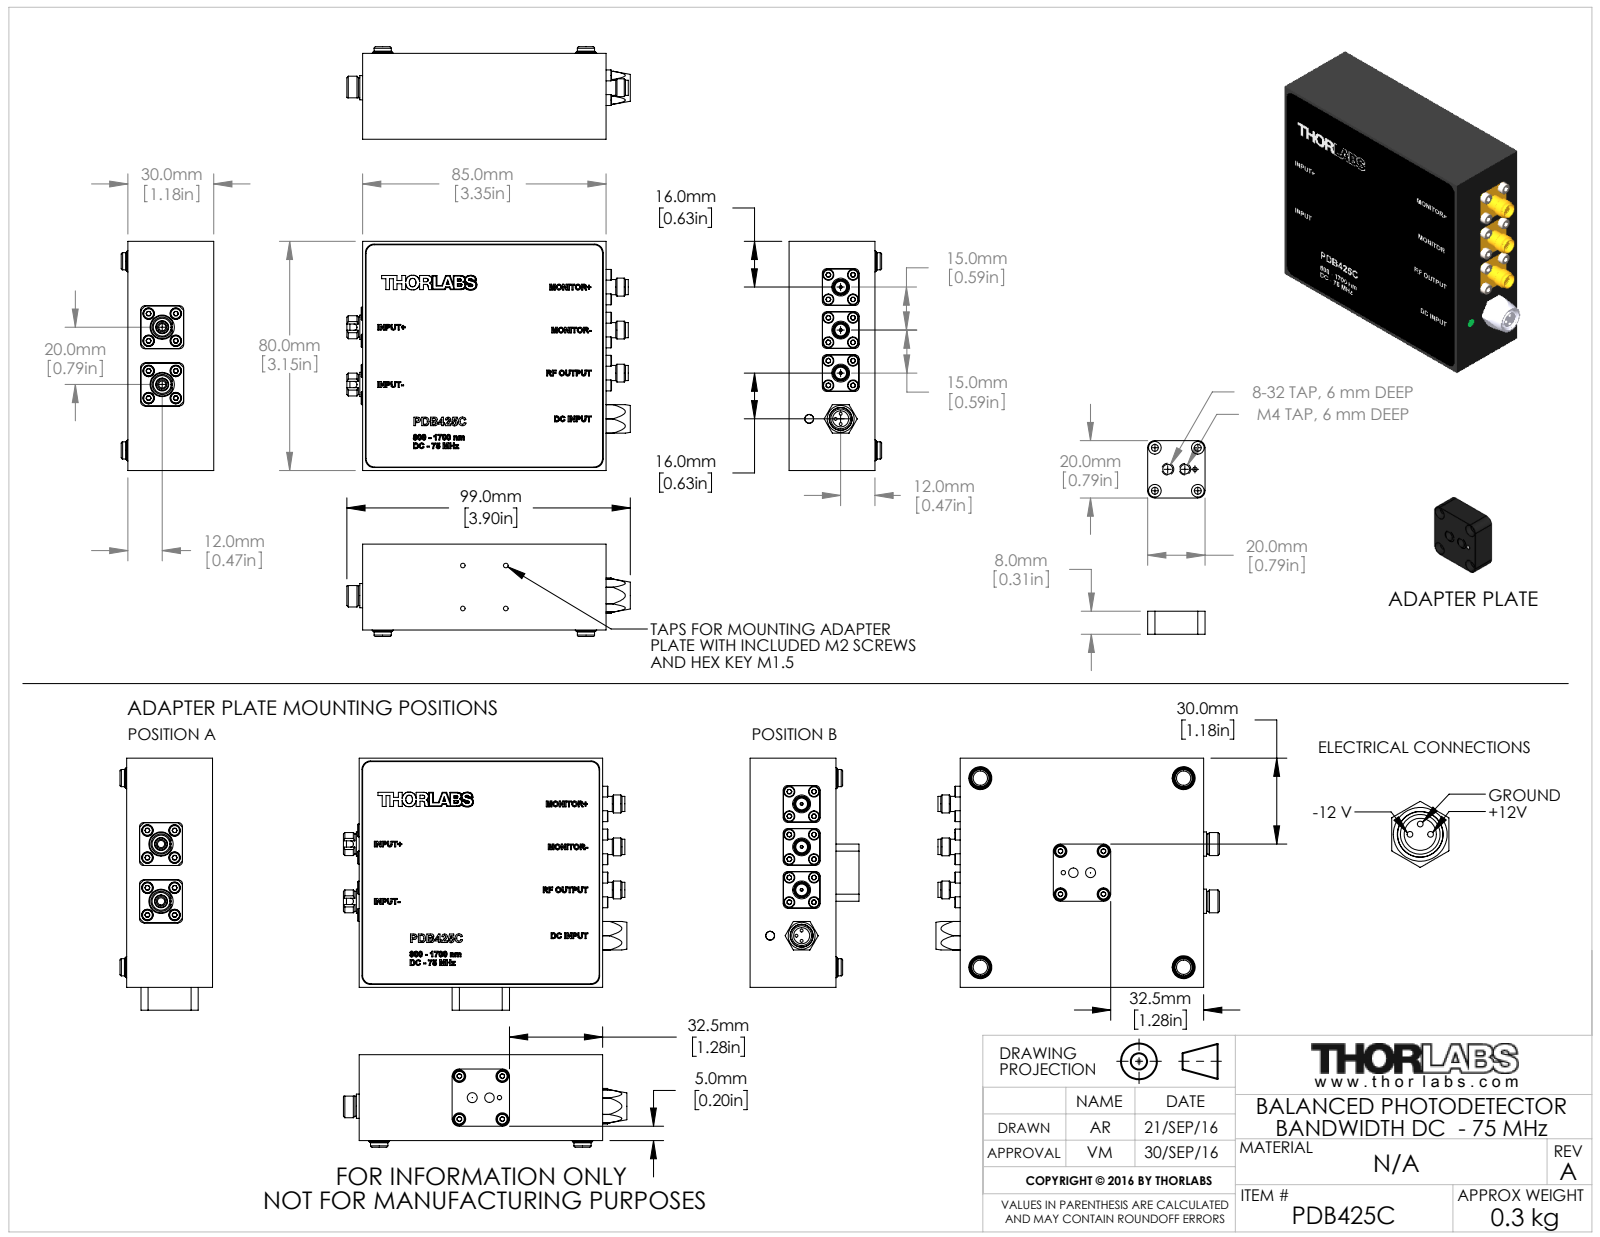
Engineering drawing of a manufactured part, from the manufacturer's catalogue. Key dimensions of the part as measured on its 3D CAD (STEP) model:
Part name (STEP PRODUCT): MTN005465-E0W
STEP written by: SolidWorks 2014 (AUTOMOTIVE_DESIGN)
Units: millimetres
Bodies: 90 solids, 3015 faces (1747 planar, 584 cylindrical, 684 other)
Overall size (bounding box): 99 × 88 × 38
Volume: 87 719 mm³ · Surface area: 57 809 mm²
Round holes (diameter × count): ⌀1.6 ×38, ⌀2.6 ×12, ⌀2.2 ×8, ⌀2.4 ×8, ⌀4 ×8, ⌀4.4 ×8, ⌀1.02 ×6, ⌀8 ×5, ⌀0.8 ×3, ⌀1 ×3, ⌀4.1 ×3, ⌀4.2 ×3
Round bosses / shafts (diameter × count): ⌀3.8 ×20, ⌀2 ×20, ⌀4.5 ×8, ⌀2.5 ×8, ⌀0.43 ×6, ⌀6 ×4, ⌀6.22 ×3, ⌀5.3 ×3
Partial cylindrical surfaces — rounded edges, fillets, slot ends (radius × count): R1.5 ×20, R3 ×12, R2.5 ×8, R5 ×8, R1 ×4, R9.5 ×2, R5.75 ×1
Main face-to-face distances: 29.7, 6, 23.7, 5.5, 80, 2, 74.5, 85, 3.5, 83
Hole centre spacings: 15, 6.08, 8.6, 9.5, 6.72, 8.75, 11.53, 12.9
